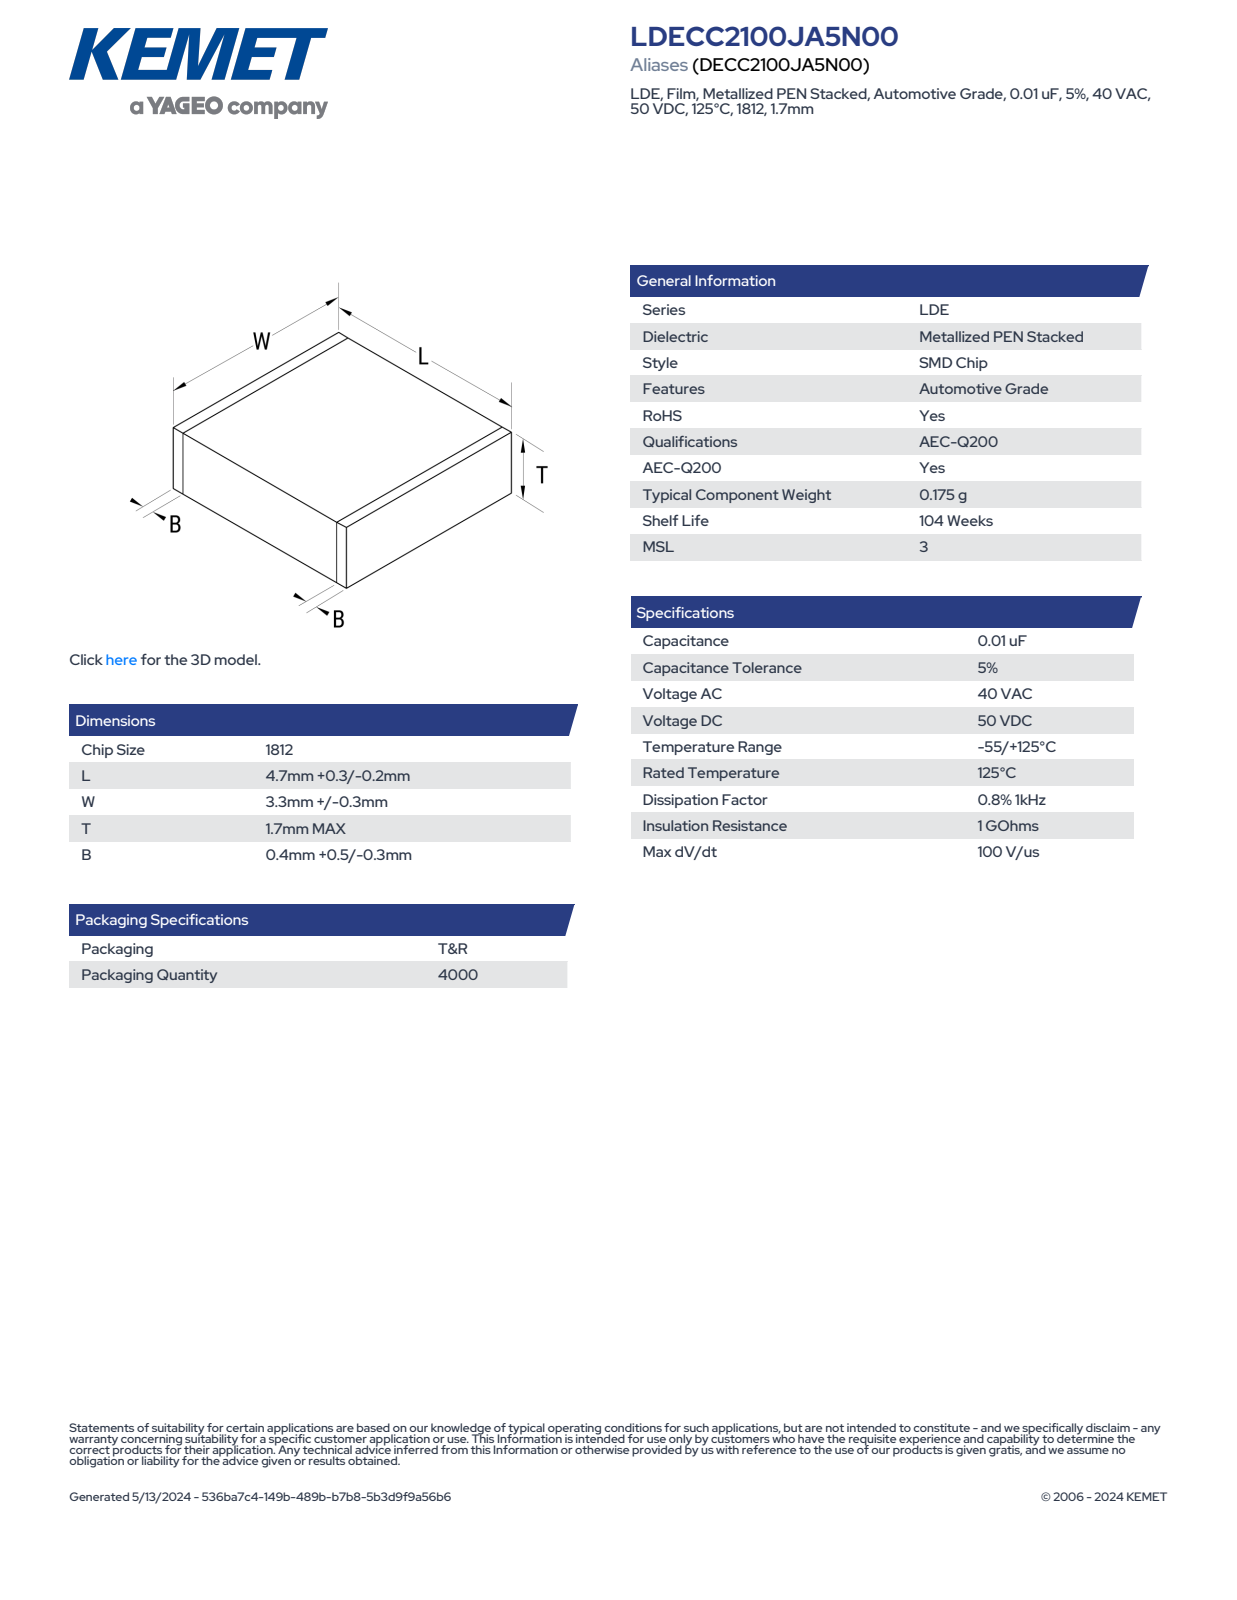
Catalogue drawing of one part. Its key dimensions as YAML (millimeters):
part_name: "CFS_LDELDB_1812_L5W3.6T1.7B0.9"
step_written_by: "SolidWorks 2020 (AUTOMOTIVE_DESIGN)"
units: millimeters
bodies: {solids: 4, faces: 73, planar: 73, cylindrical: 0, other: 0}
overall_size: [5, 3.6, 1.7]
volume: 30
surface_area: 66
face_to_face_distances: [1.68, 1.69, 3.58, 5, 1.7, 3.59, 3.6, 0.5, 4.5, 4]
